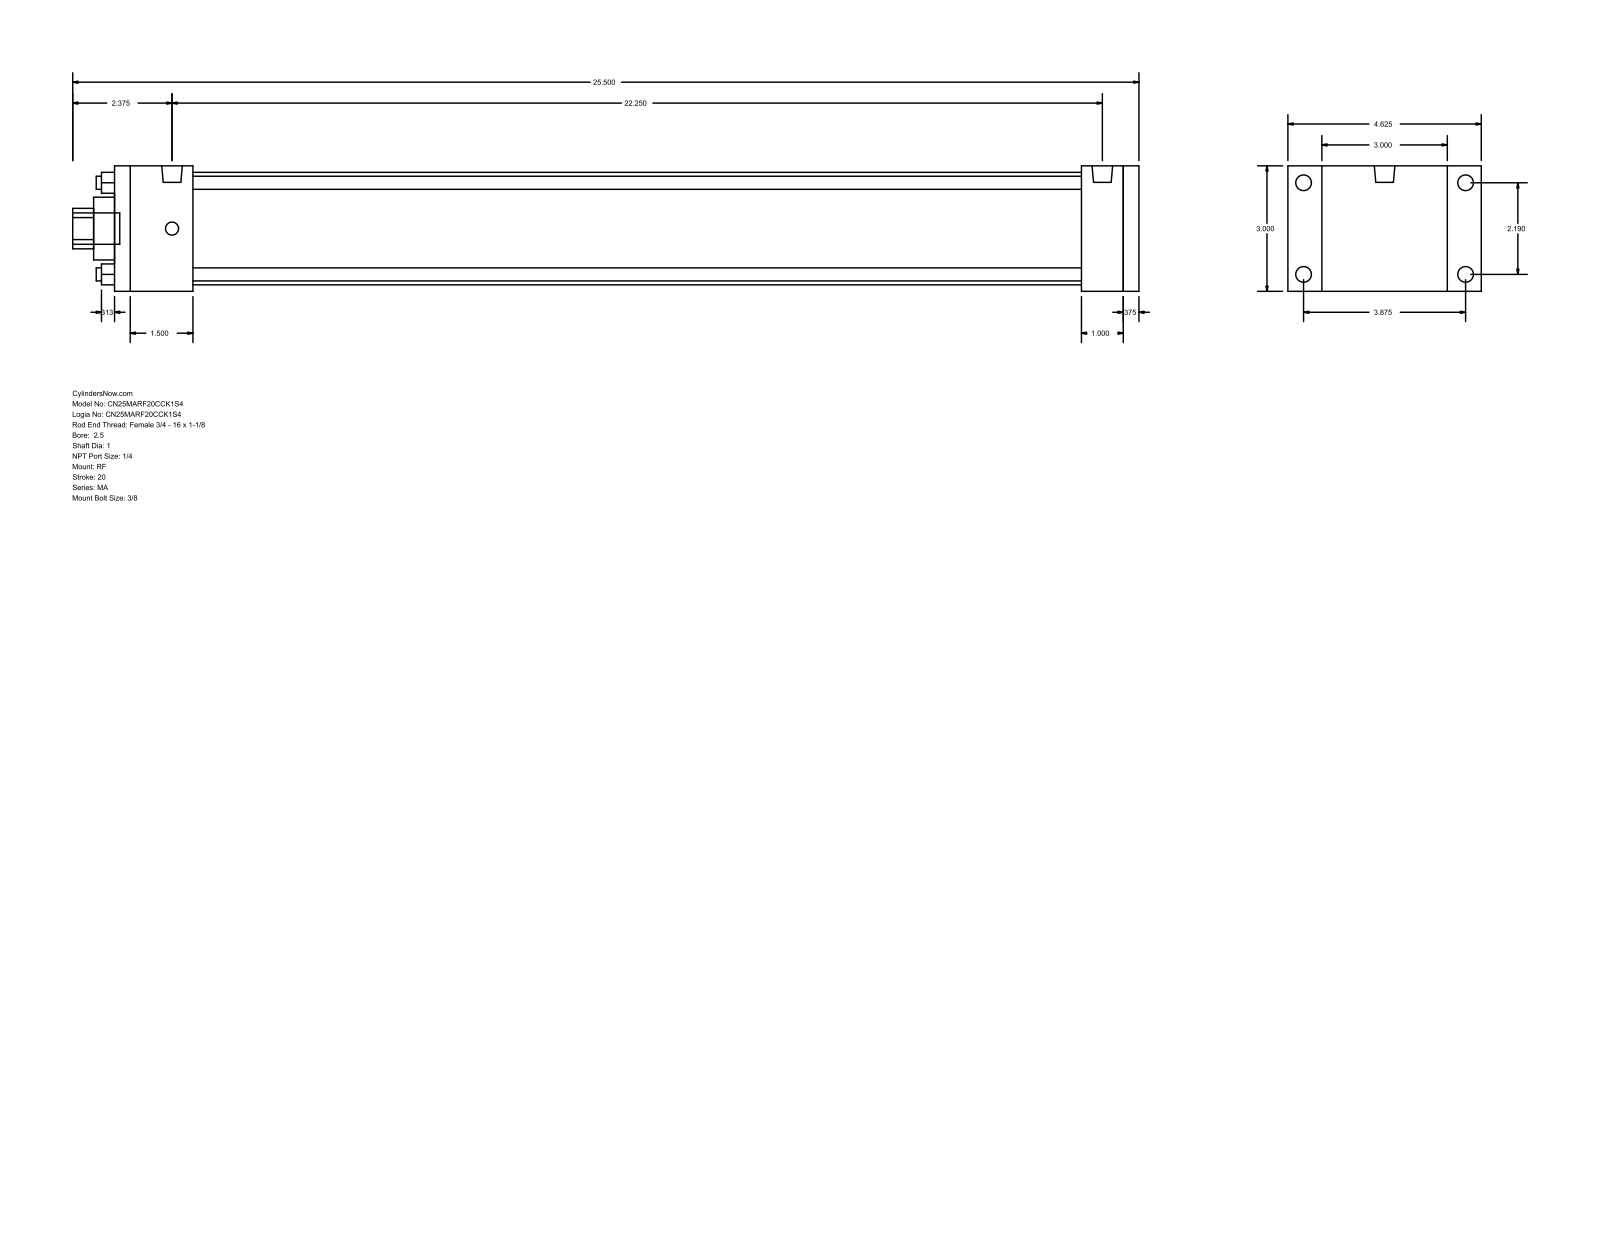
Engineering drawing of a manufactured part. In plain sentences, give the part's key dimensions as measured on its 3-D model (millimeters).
The part is named "MA_RF__0250_1". Its 3-D file was written by "GSSL Pune (CONFIG_CONTROL_DESIGN)". It is 0 solids with 92 faces: 64 planar, 28 cylindrical and 0 other. Overall it measures 647.7 by 117.47 by 76.2 millimeters. Round holes: 4 of diameter 7.94, 1 of diameter 25.4, 1 of diameter 38.1, 1 of diameter 68.33. Round bosses or shafts: 4 of diameter 9.53, 4 of diameter 7.94, 2 of diameter 12.49, 1 of diameter 19.05. Partial cylindrical surfaces (rounded edges, fillets, slot ends): 1 of radius 12.29. The main face-to-face distances are 76.2, 622.3, 612.77, 9.53, 25.4, 47.63, 587.37, 539.74, 565.14, 574.67. The hole center spacings are 39.33, 55.62, 78.66.
